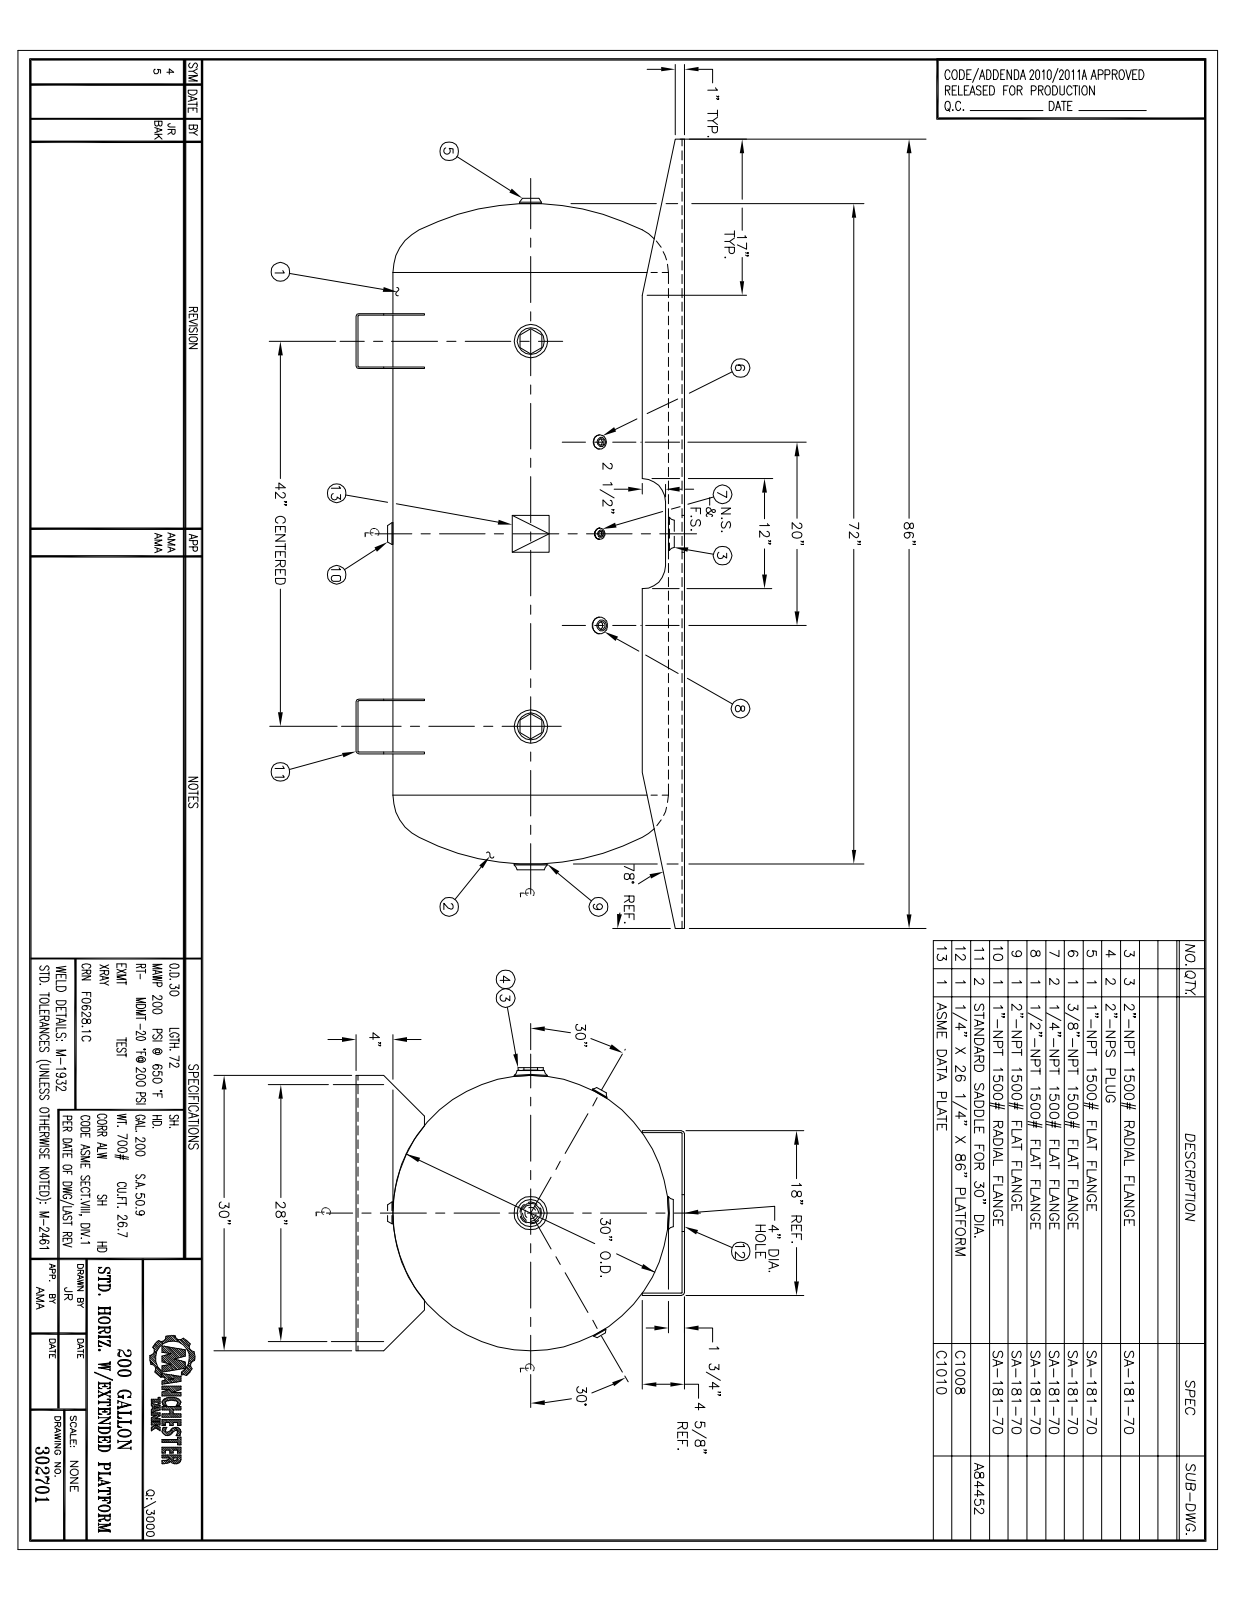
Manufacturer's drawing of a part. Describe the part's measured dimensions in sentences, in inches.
The part is named "302701". Its 3-D file was written by "SolidWorks 2012 (CONFIG_CONTROL_DESIGN)". It is 0 solids with 262 faces: 95 planar, 85 cylindrical and 82 other. Overall it measures 86 by 35.79 by 31.541 inches. Round holes: 2 of diameter 0.54, 2 of diameter 1.315, 2 of diameter 2.375, 1 of diameter 0.675, 1 of diameter 0.84, 1 of diameter 1.063, 1 of diameter 4, 1 of diameter 29.546. Round bosses or shafts: 2 of diameter 3, 2 of diameter 2.375, 2 of diameter 1.5, 1 of diameter 30, 1 of diameter 29.63, 1 of diameter 3.5, 1 of diameter 2.875, 1 of diameter 1.813. Partial cylindrical surfaces (rounded edges, fillets, slot ends): 8 of radius 0.375, 6 of radius 0.25, 4 of radius 0.437, 2 of radius 0.474, 2 of radius 2.5, 1 of radius 15.06. The main face-to-face distances are 0.224, 0.187, 42, 5.813, 17.776, 35.566, 35.79, 35.379, 35.603, 6. The hole center spacings are 10, 20.
